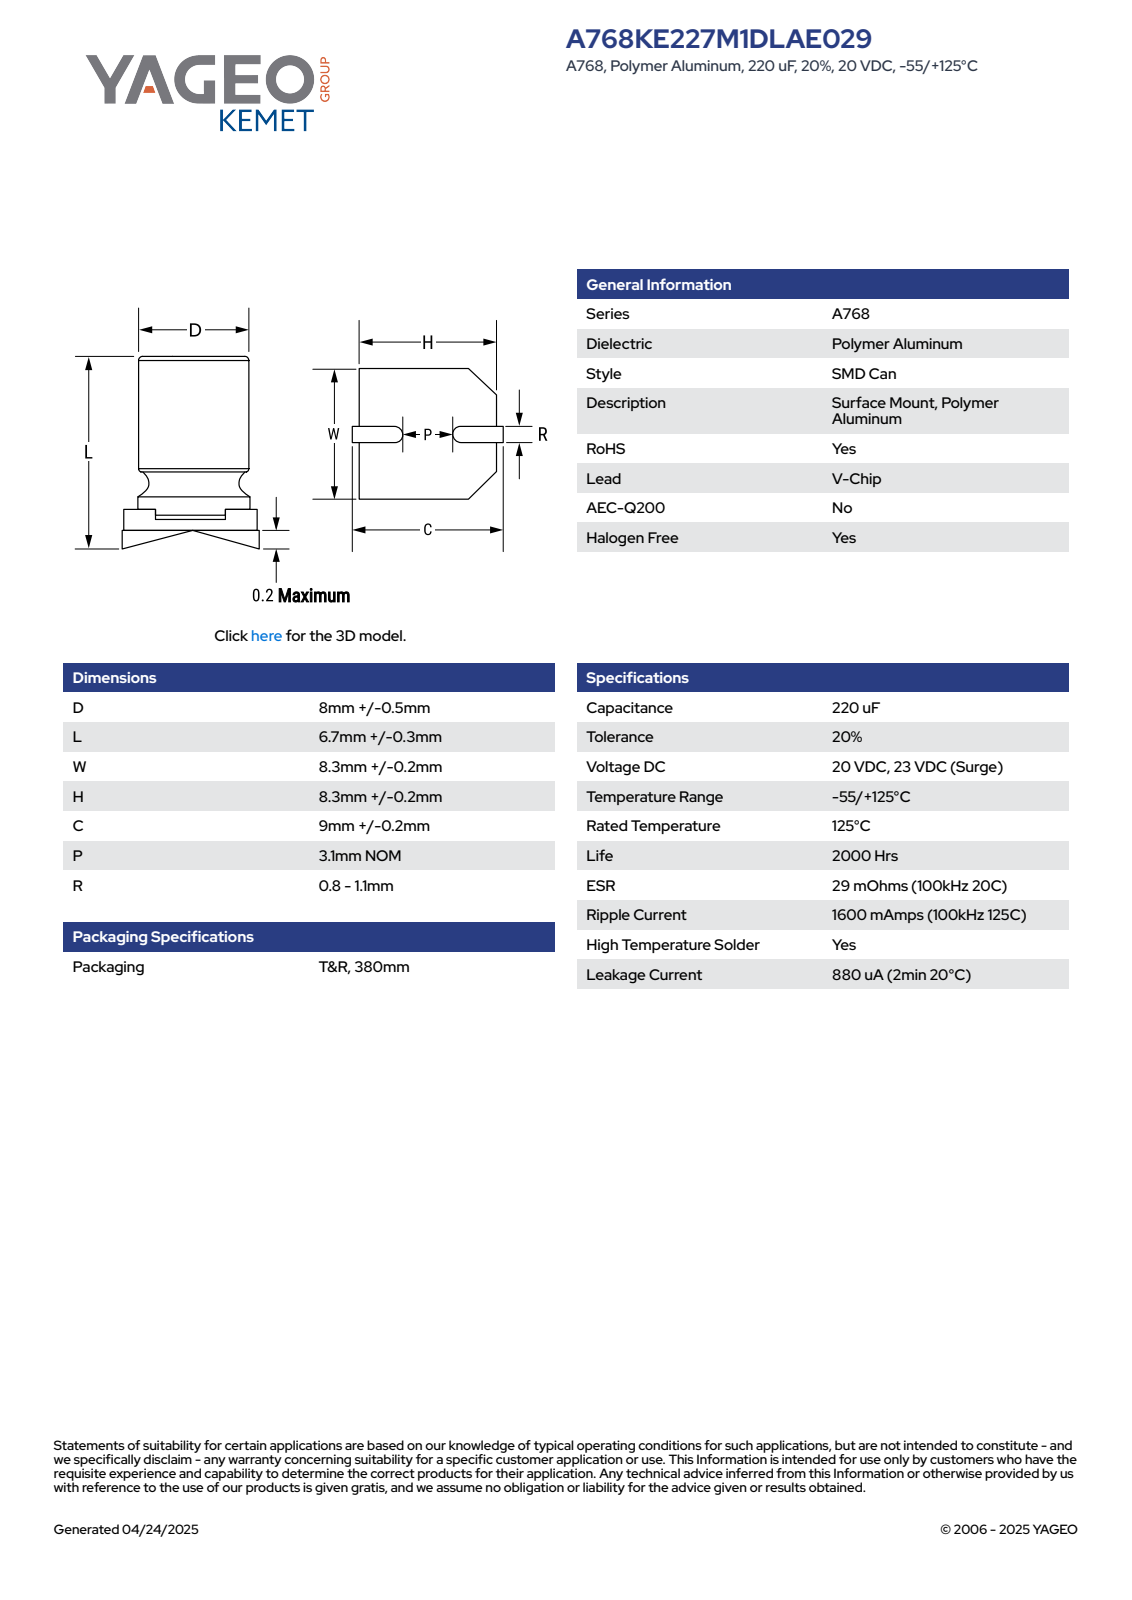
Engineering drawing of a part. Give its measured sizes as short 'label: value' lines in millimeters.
name: CAC_KSA_8X6.7_D8.5L7H8.5C9.2P3.1W8.5R1.1
written by: SolidWorks 2020 (AUTOMOTIVE_DESIGN)
unit: mm
bodies: 5 solids, 76 faces (59 planar, 11 cylindrical, 6 other)
size: 9.2 × 8.5 × 7
volume: 369 mm³; area: 470 mm²
bosses: 1× ⌀8.13
rounds: 2× R0.2, 1× R3.38, 1× R4.25
face distances: 0.35, 6.8, 6.45, 8.5, 1.75, 1.4, 5.05, 0.55, 1.95, 7
